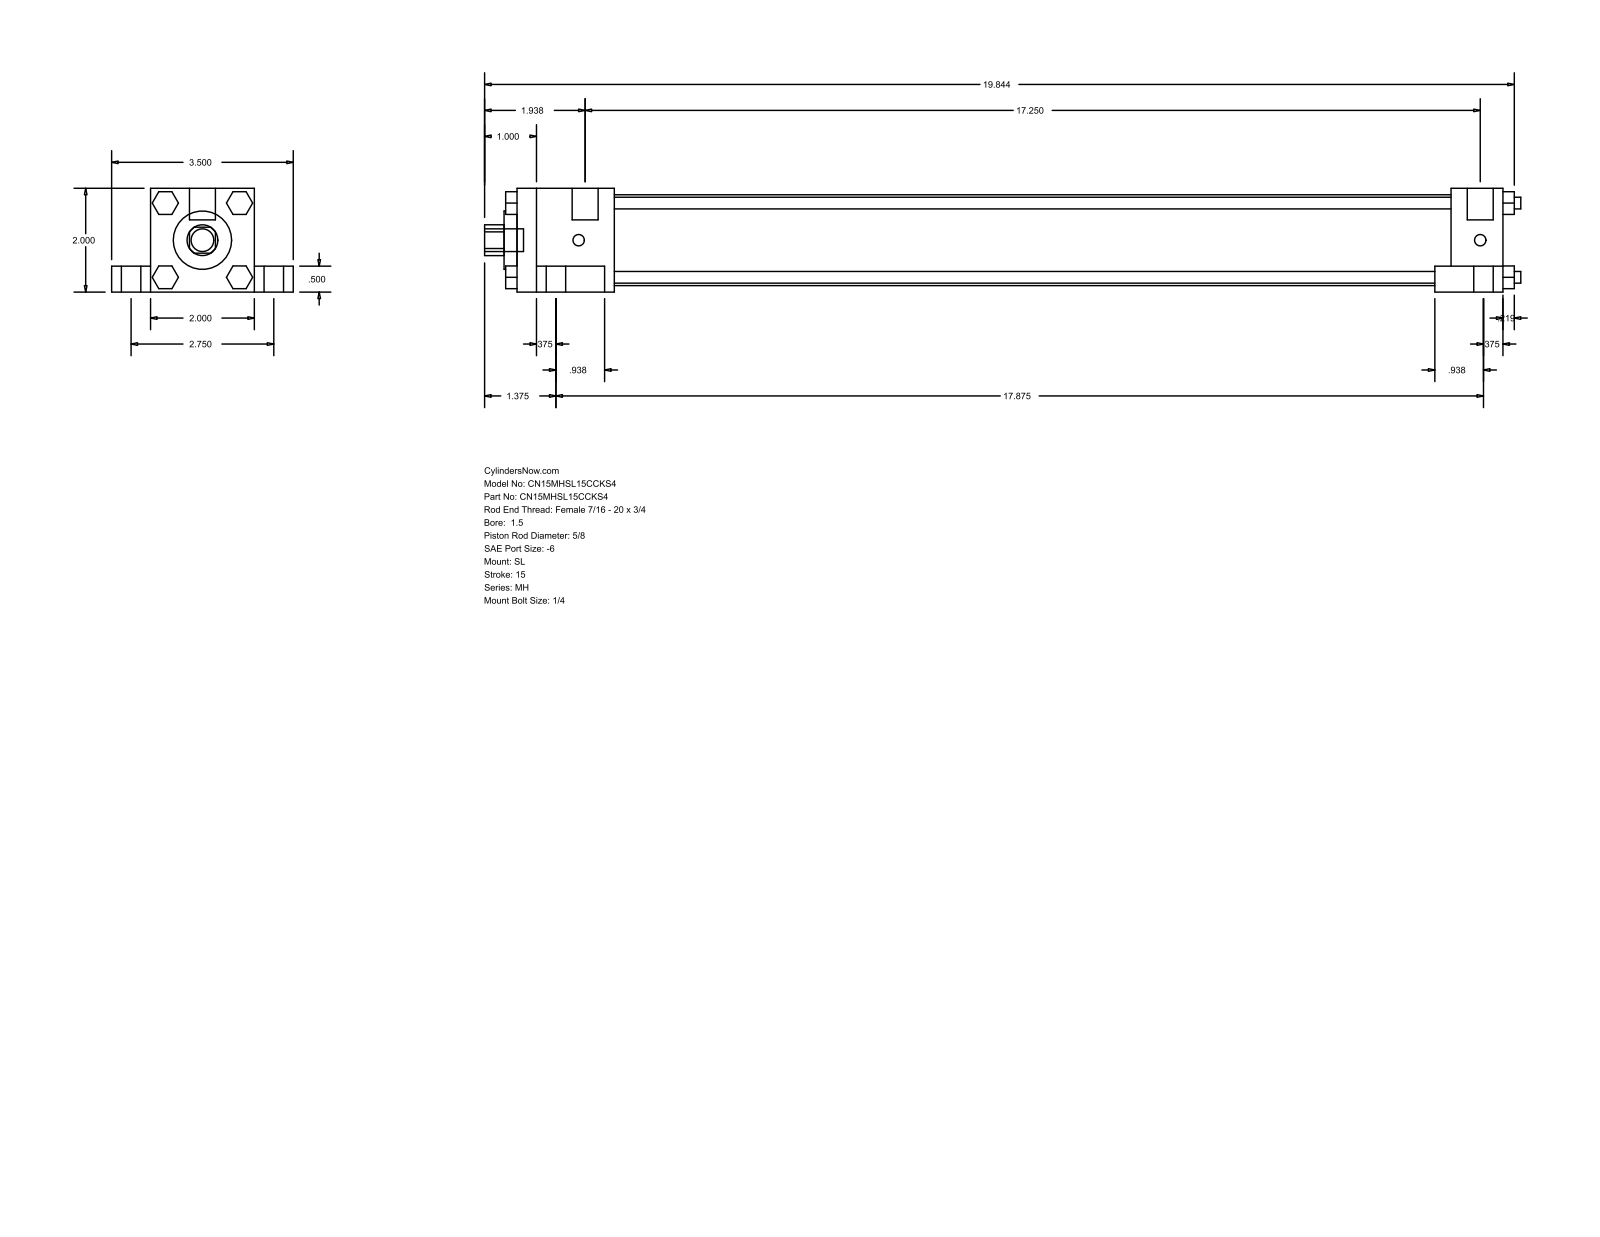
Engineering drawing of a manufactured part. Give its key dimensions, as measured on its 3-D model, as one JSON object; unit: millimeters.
{"part_name": "MH_SL__0150_0.625", "step_written_by": "GSSL Pune (CONFIG_CONTROL_DESIGN)", "units": "millimeters", "bodies": {"solids": 0, "faces": 148, "planar": 112, "cylindrical": 36, "other": 0}, "overall_size": [507.21, 88.9, 50.8], "round_holes": [[15.88, 1], [28.57, 1], [44.45, 1]], "round_bosses_or_shafts": [[15.88, 4], [9.53, 4], [5.71, 4], [5.56, 4], [12.7, 2], [11.11, 1]], "partial_cylinders_radius": [[7.54, 1]], "face_to_face_distances": [50.8, 38.1, 19.05, 12.7, 69.85, 482.6, 9.52, 33.34, 439.74, 457.19]}
